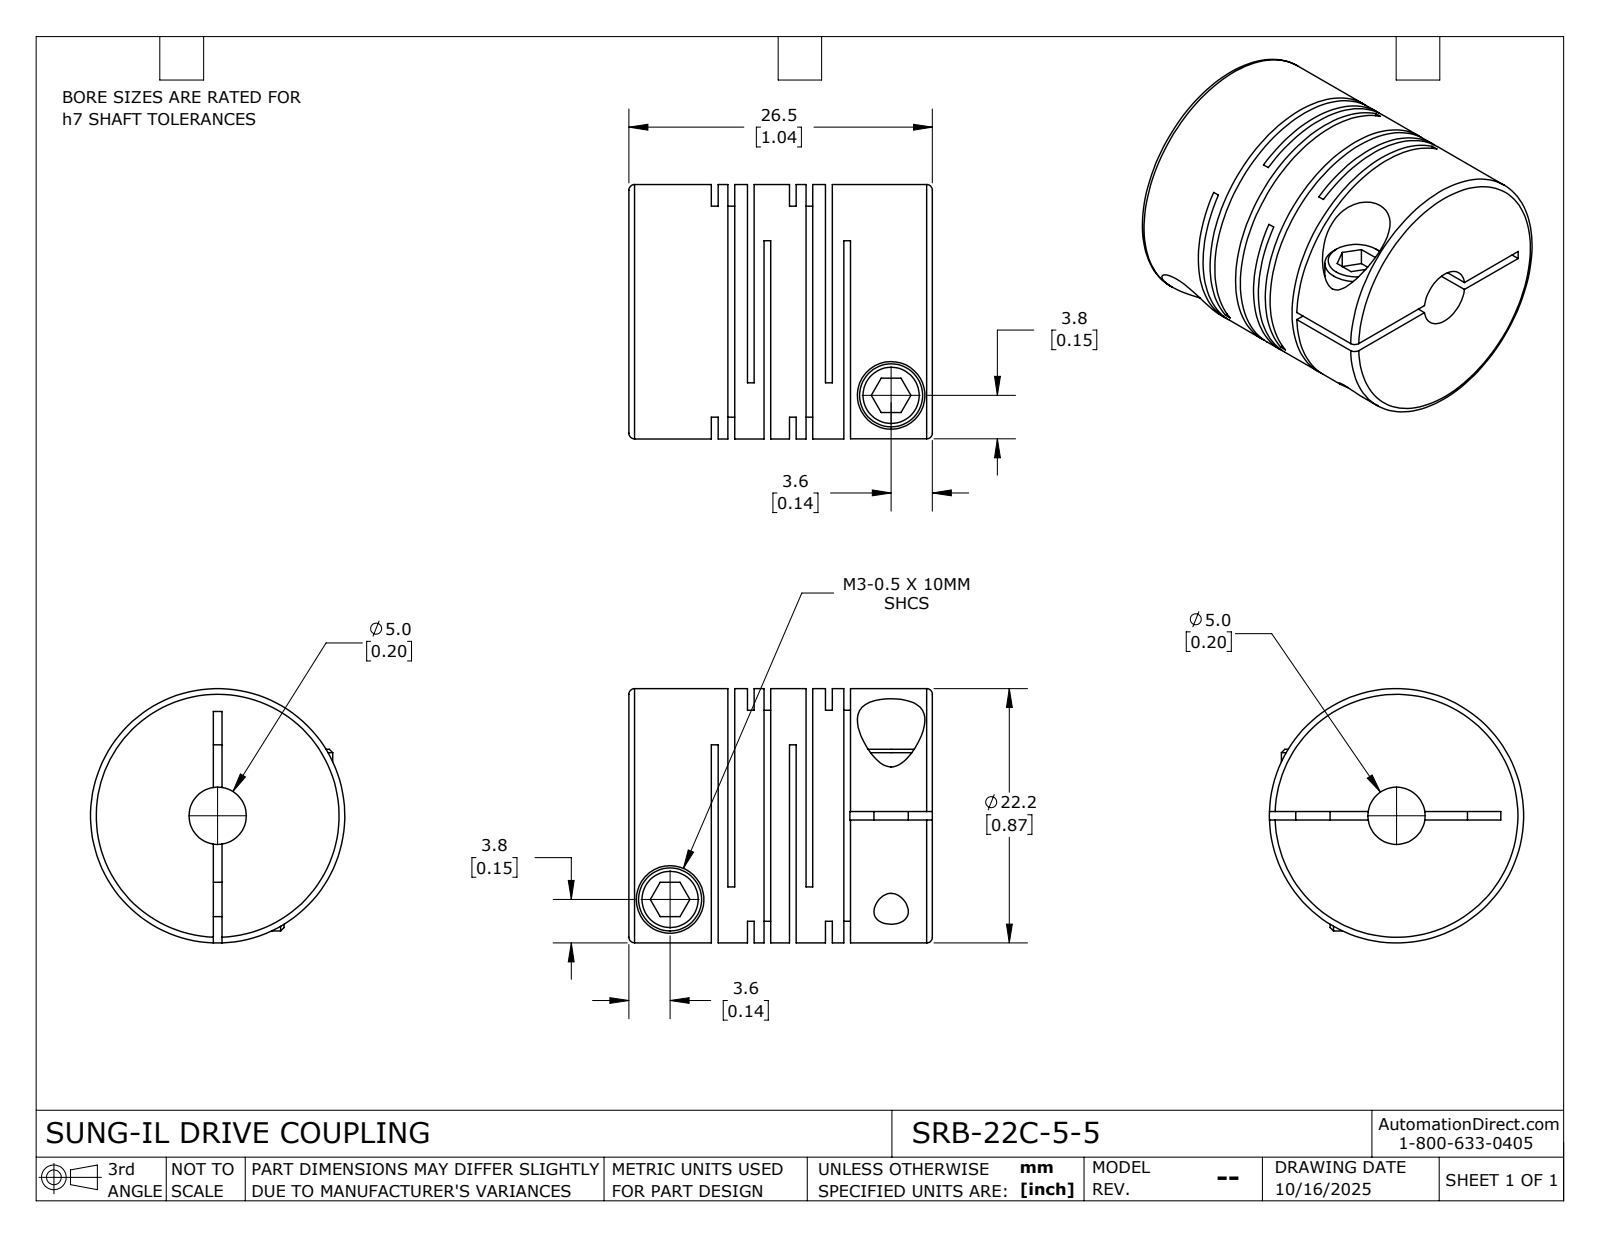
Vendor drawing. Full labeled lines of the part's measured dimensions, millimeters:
Part name (STEP PRODUCT): SRB-22C-5-5
STEP written by: SolidWorks 2024 (CONFIG_CONTROL_DESIGN)
Units: millimetres
Bodies: 1 solid, 115 faces (60 planar, 42 cylindrical, 13 other)
Overall size (bounding box): 26.5 × 22.2 × 22.2
Volume: 7 951 mm³ · Surface area: 8 264 mm²
Round holes (diameter × count): ⌀3 ×2, ⌀5.9 ×2, ⌀5 ×1
Round bosses / shafts (diameter × count): ⌀5.5 ×2, ⌀22.2 ×1
Main face-to-face distances: 0.59, 6.82, 3.15, 1.45, 5.37, 1.7, 3.67, 6.23, 0.86, 2.56
